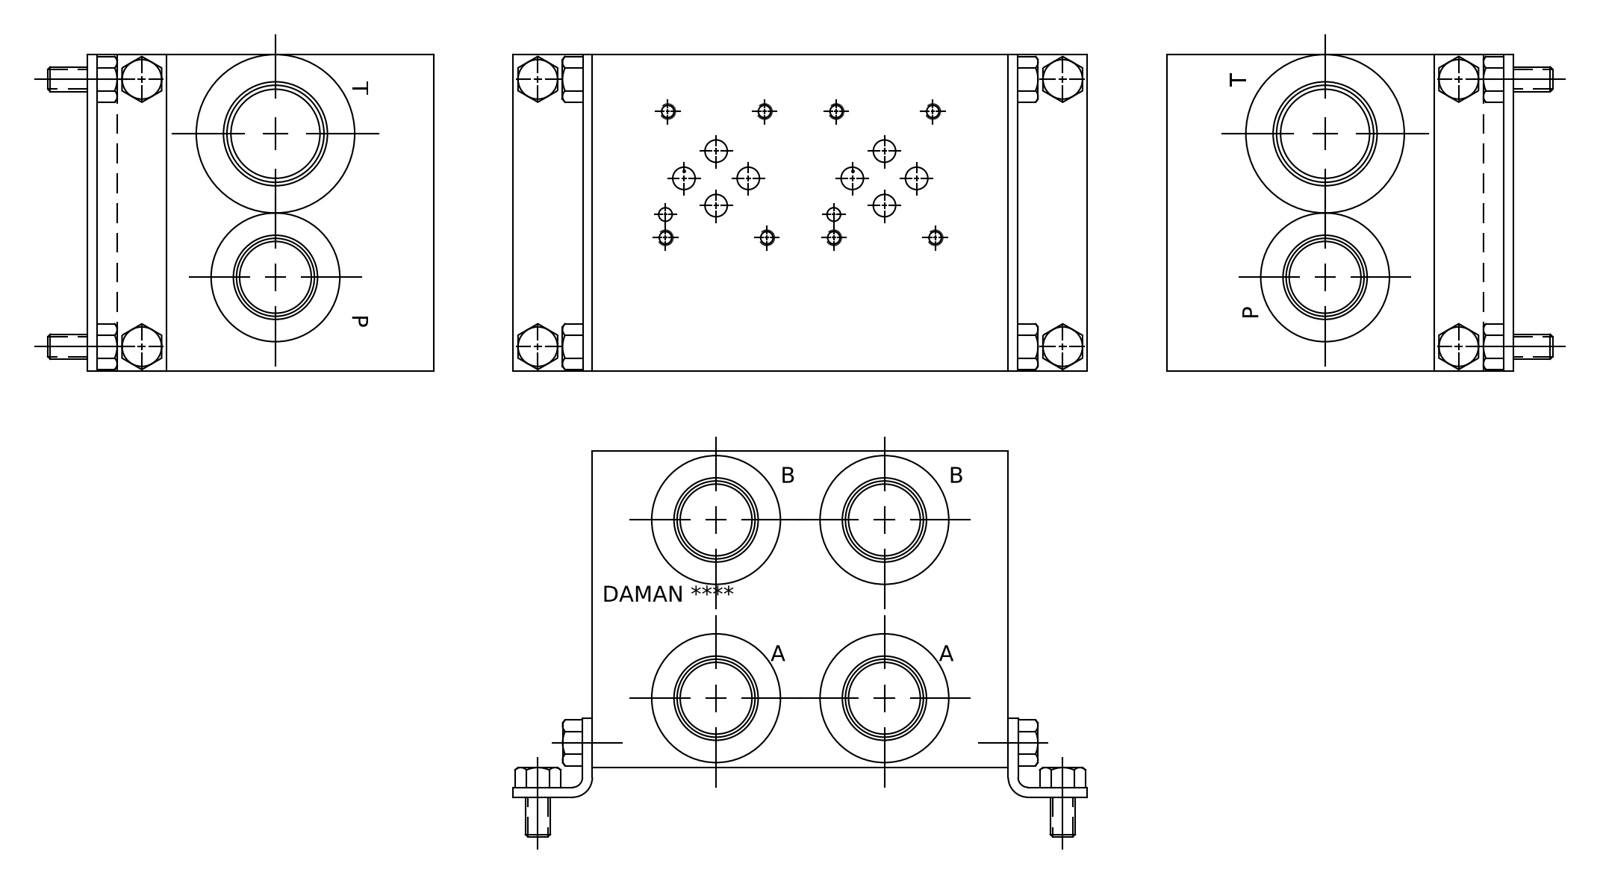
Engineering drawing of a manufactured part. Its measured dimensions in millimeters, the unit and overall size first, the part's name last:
Units: millimetres
Overall size (bounding box): 133.35 × 101.6 × 101.6
Round holes (diameter × count): ⌀3.78 ×8, ⌀4.83 ×8, ⌀7.14 ×8, ⌀24.92 ×5, ⌀29.21 ×5, ⌀41.45 ×5, ⌀23.01 ×4, ⌀26.99 ×3, ⌀3.96 ×2, ⌀6.53 ×2, ⌀7.95 ×2, ⌀10.72 ×2
Main face-to-face distances: 101.6, 133.35, 0.76, 132.59, 100.84, 131.83, 4.09, 3.33, 19.84, 19.08
Hole centre spacings: 53.98, 53.97, 13.52, 13.54, 22.05, 33.55, 40.5, 51.45
Volume: 1 148 000 mm³ · Surface area: 111 782 mm²
Bodies: 1 solid, 158 faces (42 planar, 76 cylindrical, 40 other)
Part name (STEP PRODUCT): Part_AD03HP022S_C_3D
STEP written by: Autodesk Inventor 2020 (CONFIG_CONTROL_DESIGN)
